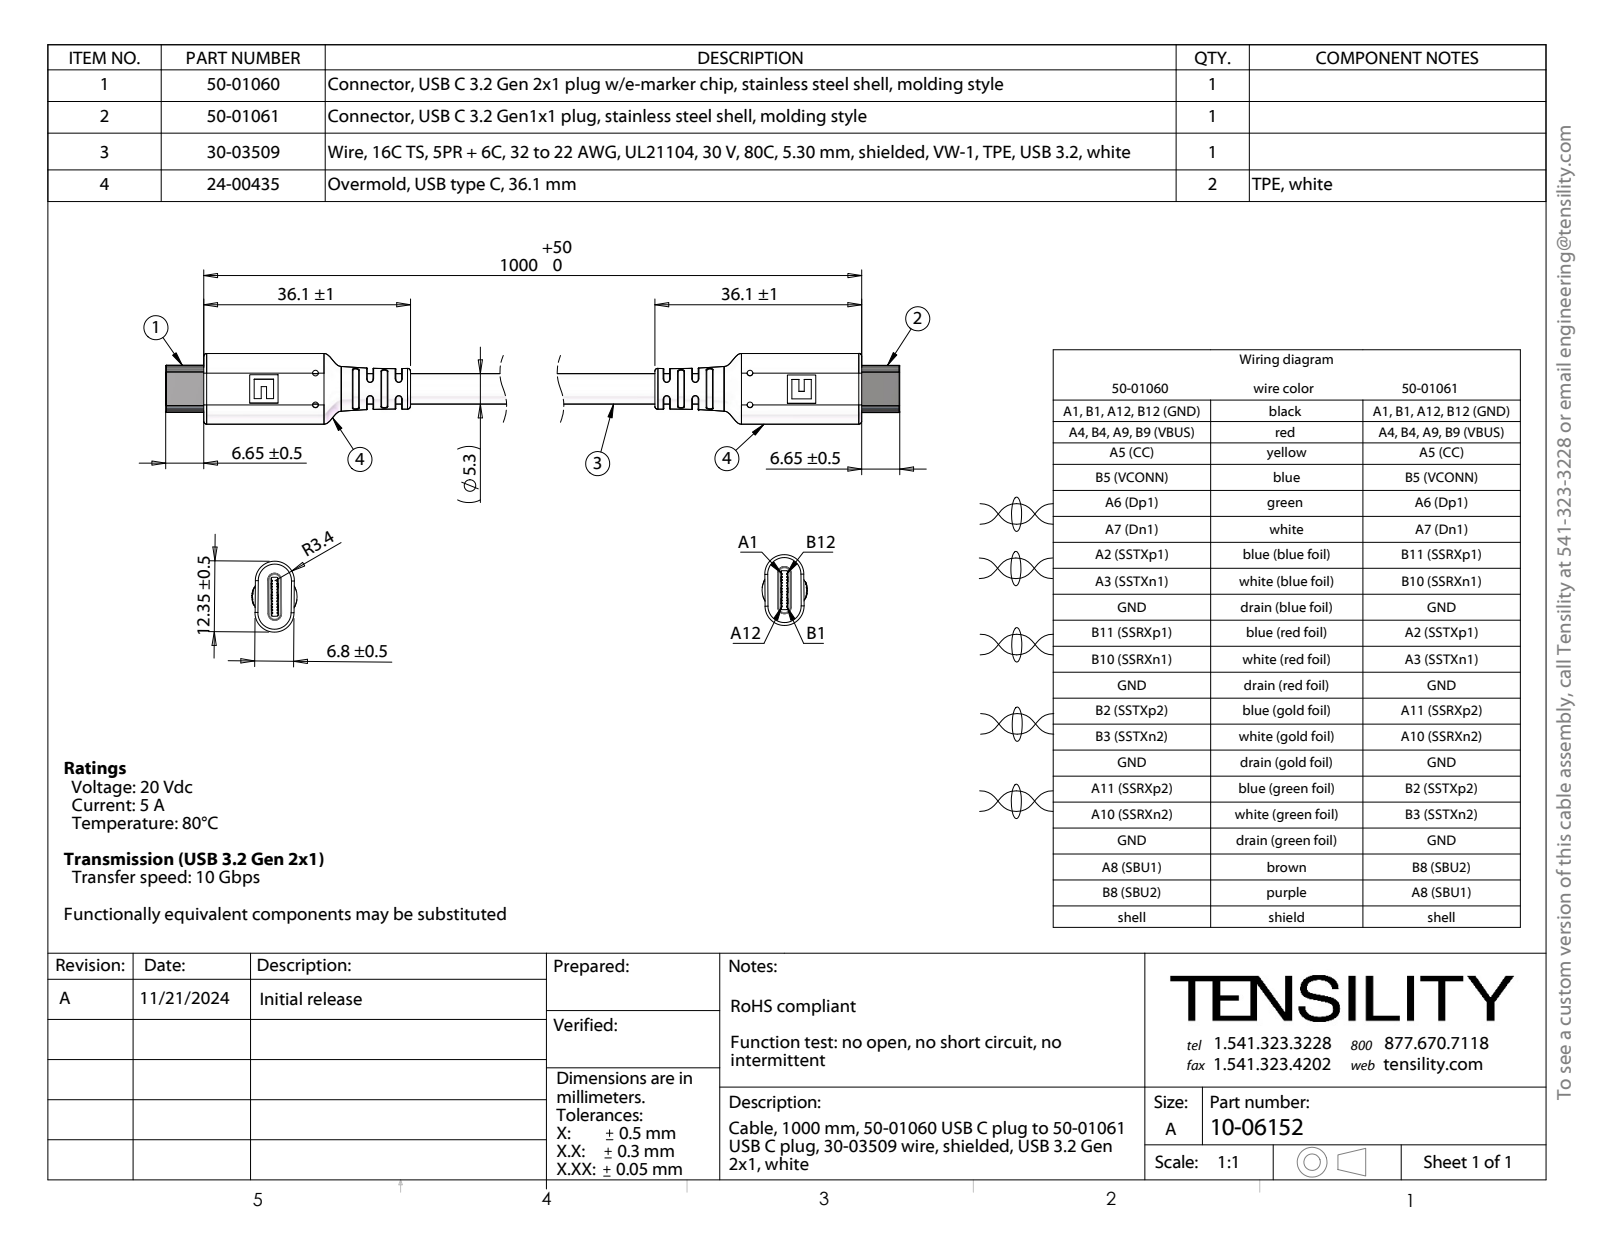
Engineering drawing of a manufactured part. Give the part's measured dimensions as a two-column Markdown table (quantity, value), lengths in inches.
| quantity | value |
| --- | --- |
| part name | 24-00435; 50-01061; 30-03509; 50-01060 (+2 more) |
| STEP written by | SolidWorks 2021 (CONFIG_CONTROL_DESIGN) |
| units | inches |
| bodies | 168 solids, 2309 faces (1091 planar, 918 cylindrical, 300 other) |
| overall size | 7.675 × 0.486 × 0.311 |
| volume | 0.419 in³ |
| surface area | 77.12 in² |
| round holes (diameter × count) | 0.039 × 4, 0.164 × 1, 0.164 × 1, 0.165 × 1, 0.165 × 1, 0.173 × 1 |
| round bosses / shafts (diameter × count) | 0.029 × 8, 0.019 × 4, 0.01 × 4, 0.022 × 2, 0.308 × 1, 0.209 × 1, 0.039 × 1, 0.035 × 1 |
| partial cylindrical surfaces (radius × count) | 0.008 × 102, 0.02 × 20, 0.01 × 12, 0.004 × 8, 0.012 × 6, 0.006 × 4, 0.016 × 4, 0.046 × 4 |
| main face-to-face distances | 0.041, 0.041, 0.038, 0.043, 0.268, 0.041, 0.024, 0.04, 0.037, 0.038 |
| hole center spacings | 0.083, 0.081, 0.084, 0.08, 0.081, 0.097, 0.098, 0.1 |
